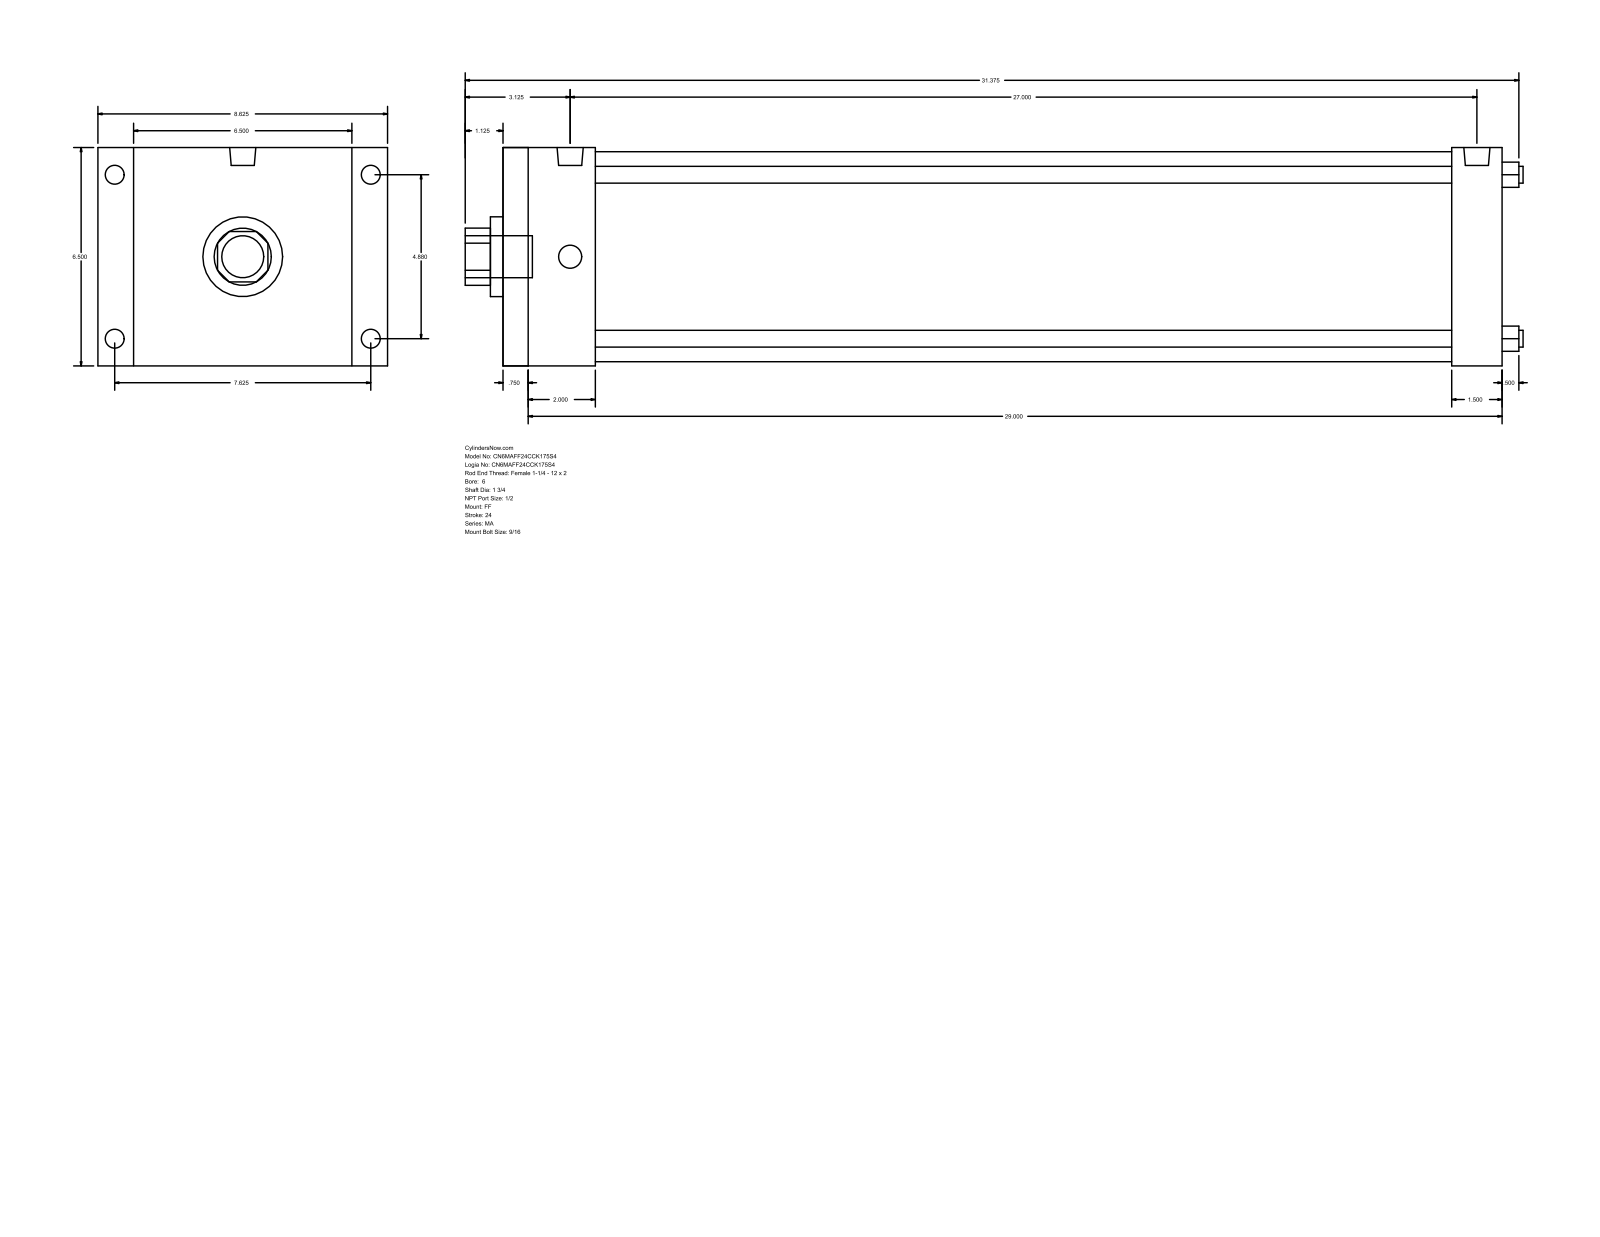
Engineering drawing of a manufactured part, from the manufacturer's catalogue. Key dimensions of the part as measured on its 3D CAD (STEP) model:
Part name (STEP PRODUCT): MA_FF__0600_1.75
STEP written by: GSSL Pune (CONFIG_CONTROL_DESIGN)
Units: millimetres
Bodies: 0 solids, 92 faces (64 planar, 28 cylindrical, 0 other)
Overall size (bounding box): 800.1 × 219.07 × 165.1
Round holes (diameter × count): ⌀12.7 ×4, ⌀44.45 ×1, ⌀60.33 ×1, ⌀158.75 ×1
Round bosses / shafts (diameter × count): ⌀17.46 ×4, ⌀14.29 ×4, ⌀19.77 ×2, ⌀31.75 ×1
Partial cylindrical surfaces — rounded edges, fillets, slot ends (radius × count): R21.63 ×1
Main face-to-face distances: 165.1, 755.66, 19.05, 736.61, 50.8, 698.5, 69.85, 685.81, 717.55, 647.7
Hole centre spacings: 87.65, 123.96, 175.31
